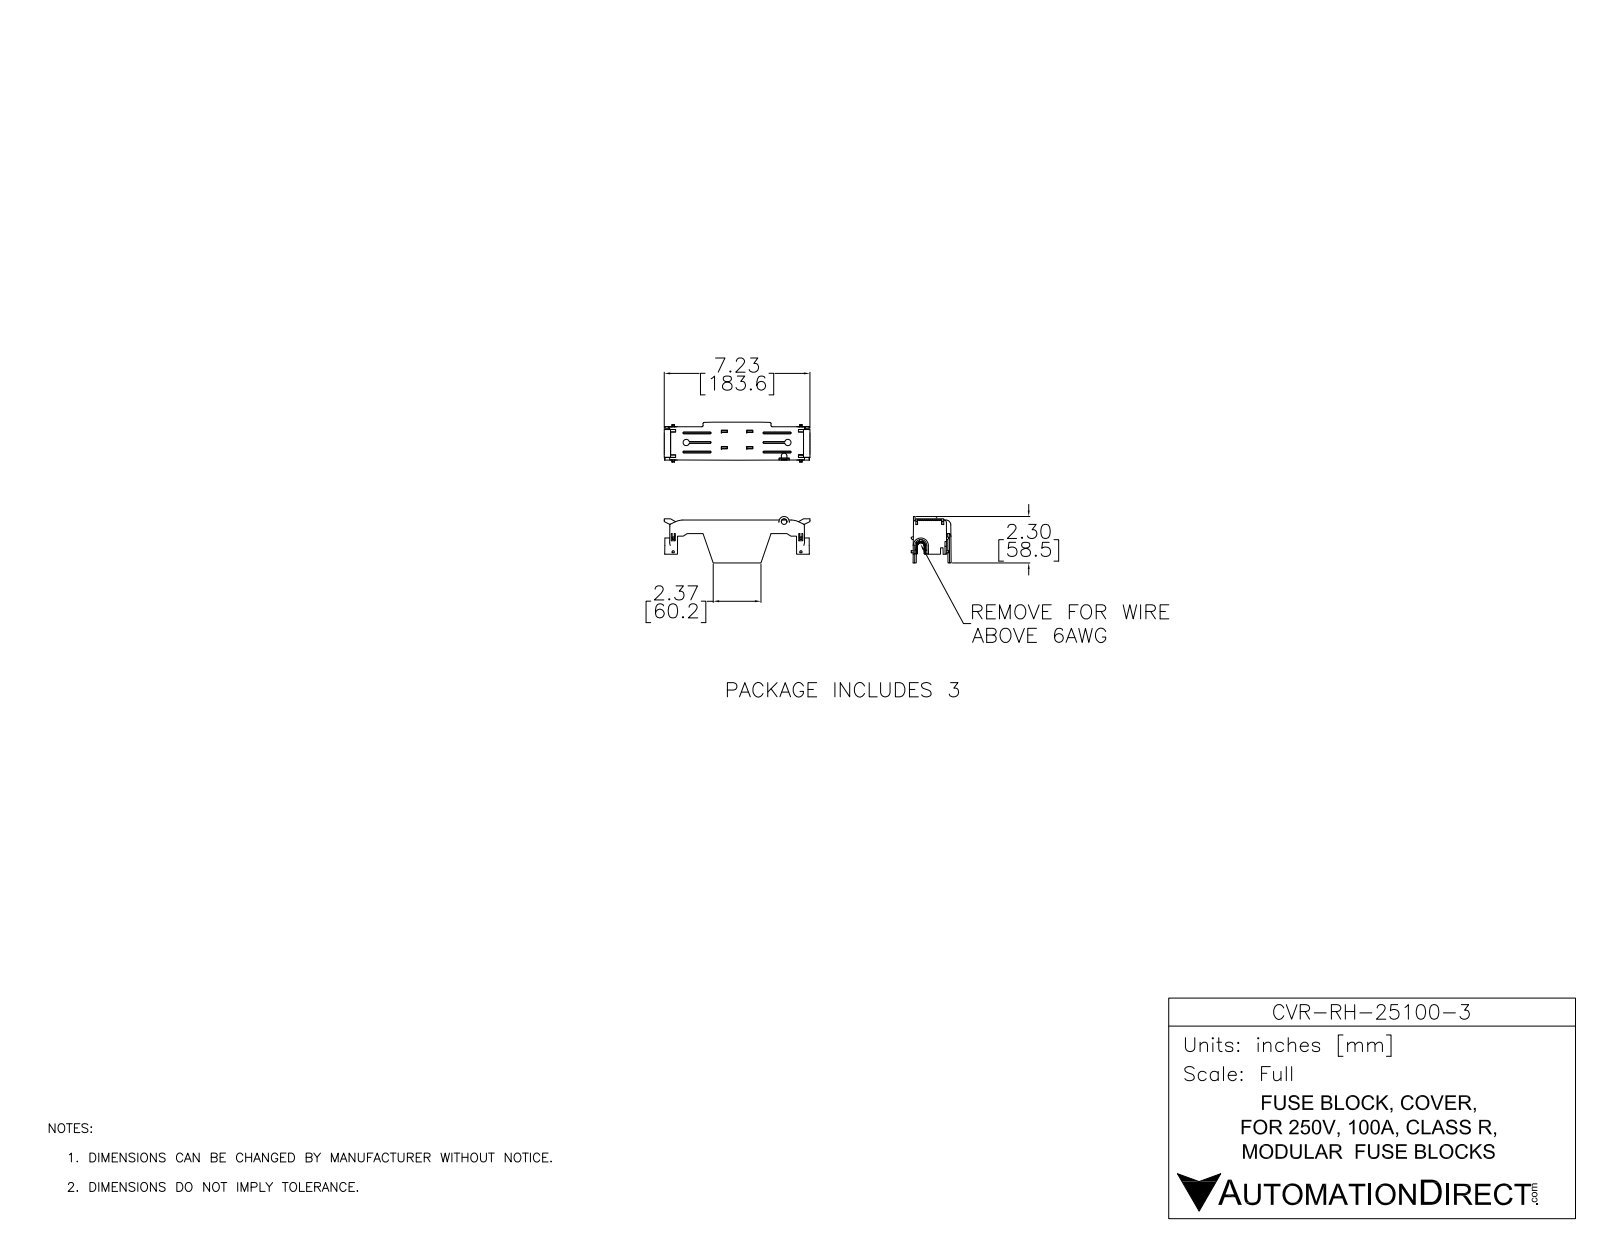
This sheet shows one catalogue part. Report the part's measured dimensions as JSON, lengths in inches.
{"part_name": "CVR-RH-25100-3", "step_written_by": "SolidWorks 2017 (AUTOMOTIVE_DESIGN)", "units": "inches", "bodies": {"solids": 1, "faces": 1324, "planar": 879, "cylindrical": 102, "other": 343}, "overall_size": [7.229, 2.304, 1.983], "volume_in3": 3.152, "surface_area_in2": 85.59, "partial_cylinders_radius": [[0.039, 18], [0.118, 14], [0.031, 6], [0.059, 4], [0.01, 2], [0.02, 2], [0.079, 2], [0.138, 2]], "face_to_face_distances": [0.079, 0.217, 0.138, 0.295, 0.567, 0.118, 0.197, 2.244, 0.346, 0.472]}
